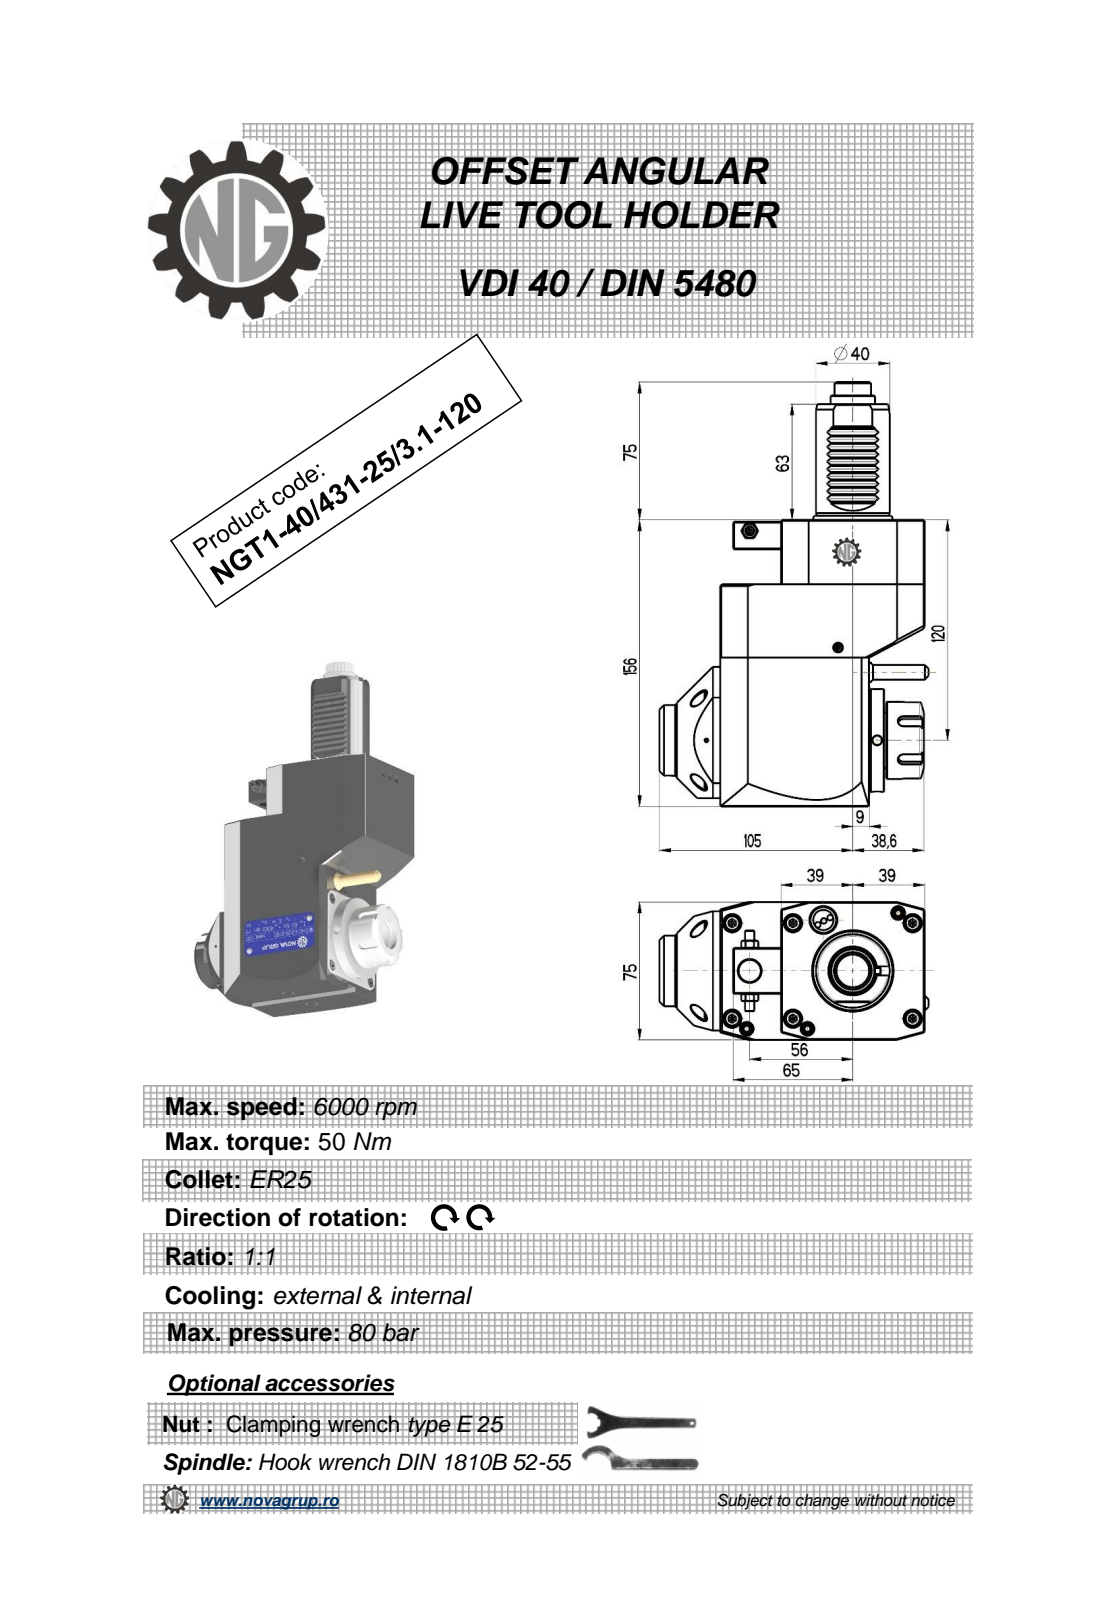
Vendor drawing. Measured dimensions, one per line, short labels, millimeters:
name: NGT1_40_431_25_3_1_120
written by: PRO/ENGINEER BY PARAMETRIC TECHNOLOGY CORPORATION, 2010280 (CONFIG_CONTROL_DESIGN)
unit: mm
bodies: 1 solid, 563 faces (207 planar, 183 cylindrical, 173 other)
size: 231 × 146.14 × 75
volume: 1 208 000 mm³; area: 89 605 mm²
holes: 3× ⌀5, 1× ⌀3, 1× ⌀4.2, 1× ⌀9.5, 1× ⌀12, 1× ⌀20.3
bosses: 1× ⌀56, 1× ⌀43, 1× ⌀42, 1× ⌀40, 1× ⌀38.5, 1× ⌀33, 1× ⌀24, 1× ⌀11.2
rounds: 48× R2.08, 12× R0.26, 10× R0.3, 6× R0.22, 5× R3, 1× R9.08, 1× R9.92, 1× R15
face distances: 75, 156, 111, 33, 35, 121, 30, 81, 48, 78
hole spacings: 40.93, 69.25, 76.53, 111.5, 133.39
